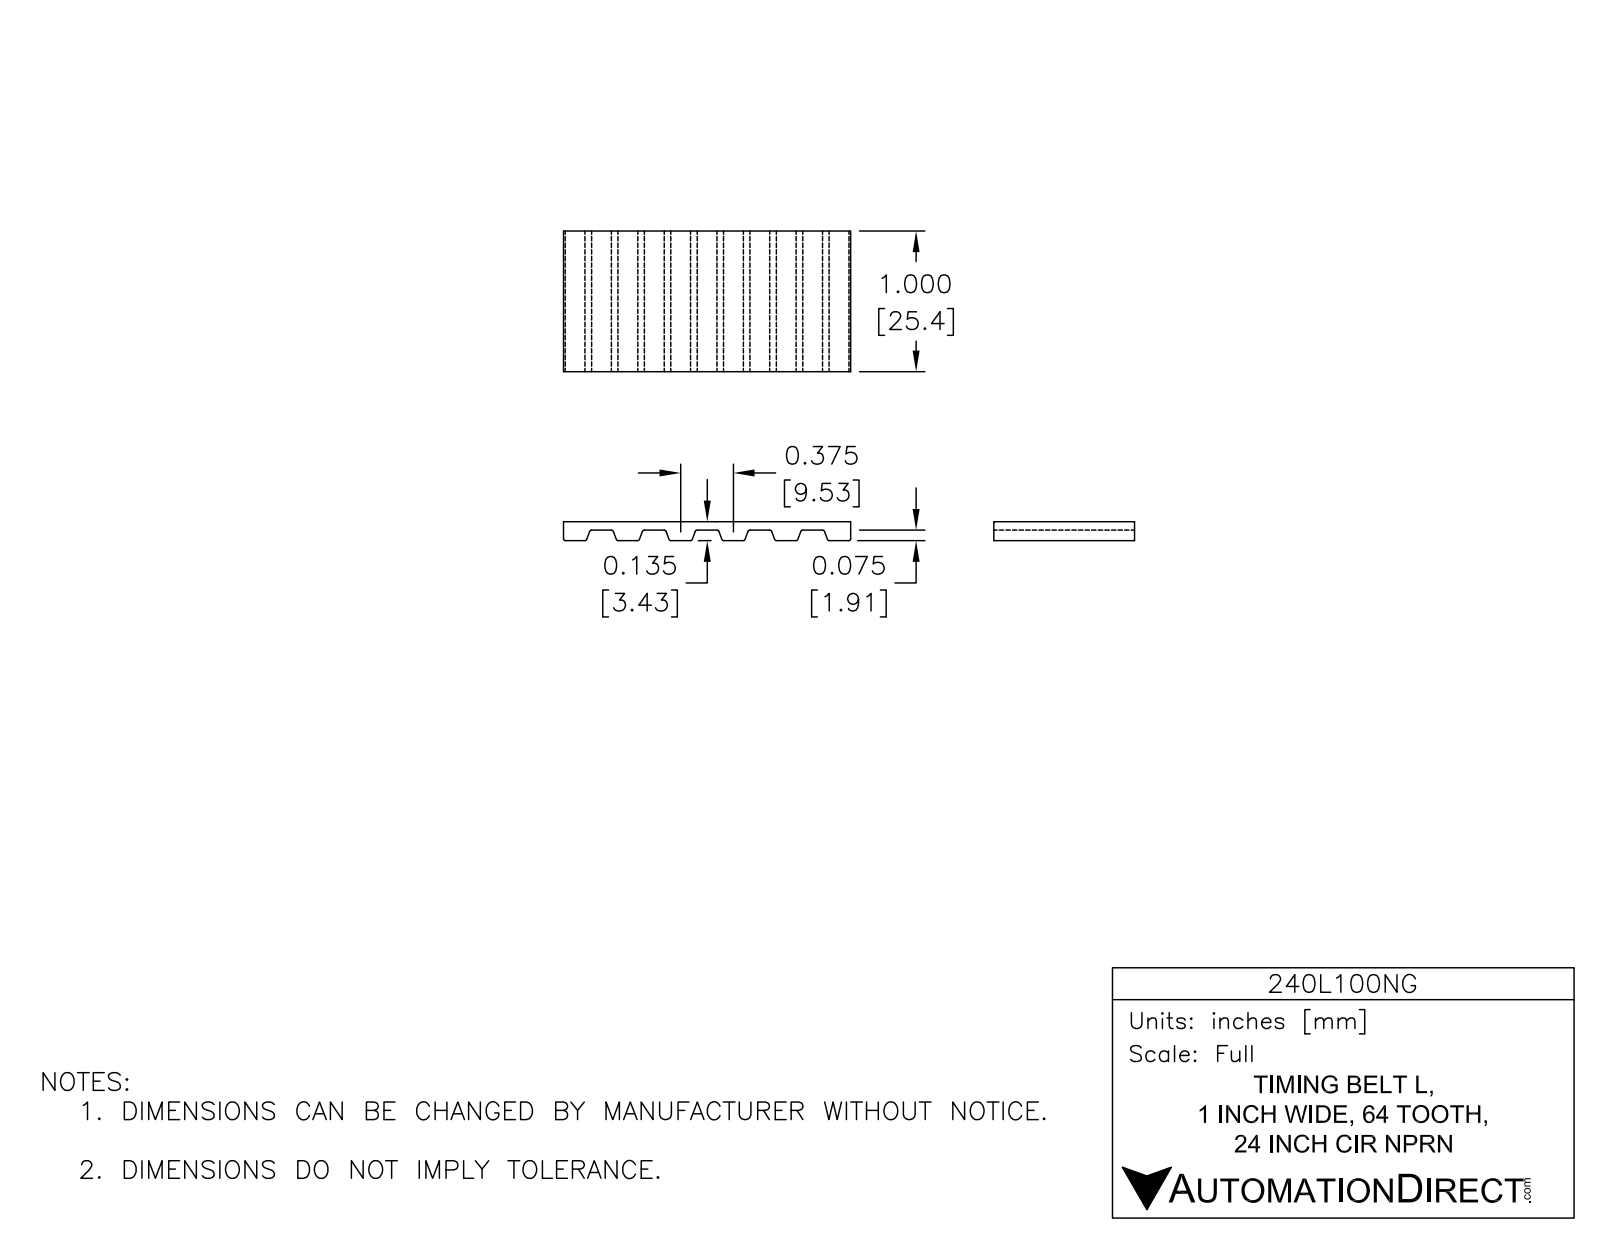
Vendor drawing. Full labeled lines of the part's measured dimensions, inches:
Part name (STEP PRODUCT): 240L100NG
STEP written by: SolidWorks 2014 (AUTOMOTIVE_DESIGN)
Units: inches
Bodies: 1 solid, 527 faces (233 planar, 294 cylindrical, 0 other)
Overall size (bounding box): 10.288 × 3 × 1
Volume: 2.164 in³ · Surface area: 57.62 in²
Partial cylindrical surfaces — rounded edges, fillets, slot ends (radius × count): R0.02 ×252, R1.435 ×2, R1.5 ×2
Main face-to-face distances: 0.065, 2.935, 3, 2.87, 0.14, 2.86, 0.075, 2.795, 1, 2.72
